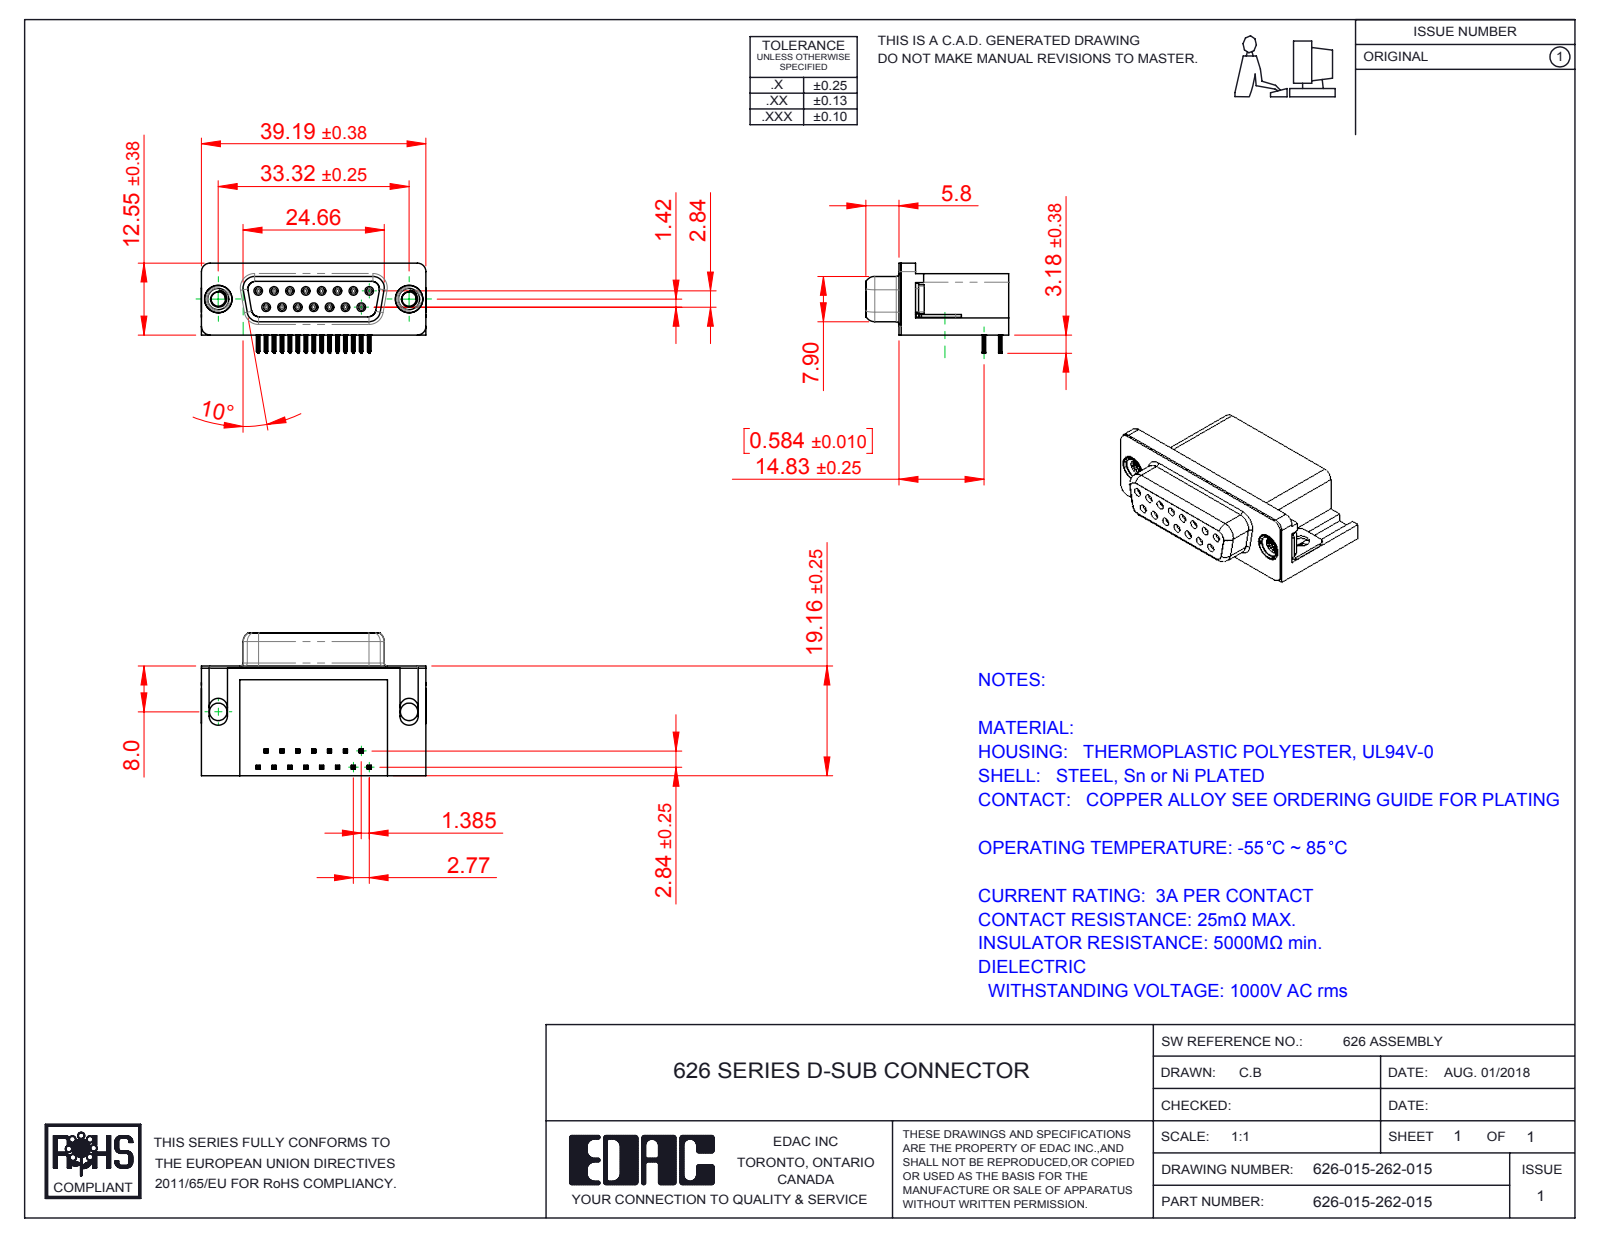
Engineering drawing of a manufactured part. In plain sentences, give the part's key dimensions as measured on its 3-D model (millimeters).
The part is named "626 Contact Bottom; 626-015-262-015; 626 Contact Top; 626 M3 Threaded Rivet (+3 more)". Its 3-D file was written by "SolidWorks 2016 (CONFIG_CONTROL_DESIGN)". It is 21 solids with 2425 faces: 1072 planar, 609 cylindrical and 744 other. Overall it measures 39.22 by 24.96 by 15.73 millimeters. Its volume is 7 238 cubic millimeters and its surface area 8 020 square millimeters. Round holes: 15 of diameter 0.8, 15 of diameter 0.9, 2 of diameter 2.5, 2 of diameter 3.05, 2 of diameter 4, 2 of diameter 4.8, 2 of diameter 5. Round bosses or shafts: 15 of diameter 1.2, 2 of diameter 4.9, 2 of diameter 4.75, 2 of diameter 3.9. Partial cylindrical surfaces (rounded edges, fillets, slot ends): 120 of radius 0.1, 60 of radius 0.15, 30 of radius 0.35, 18 of radius 1, 15 of radius 0.34, 8 of radius 0.25, 8 of radius 1.35, 8 of radius 1.6. The main face-to-face distances are 0.4, 10.35, 0.35, 18.76, 2.73, 6.2, 19.16, 10.7, 9.38, 3.18. The hole center spacings are 3.16, 2.77, 5.54, 8.31, 11.08, 5.03, 5.04, 7.48.
